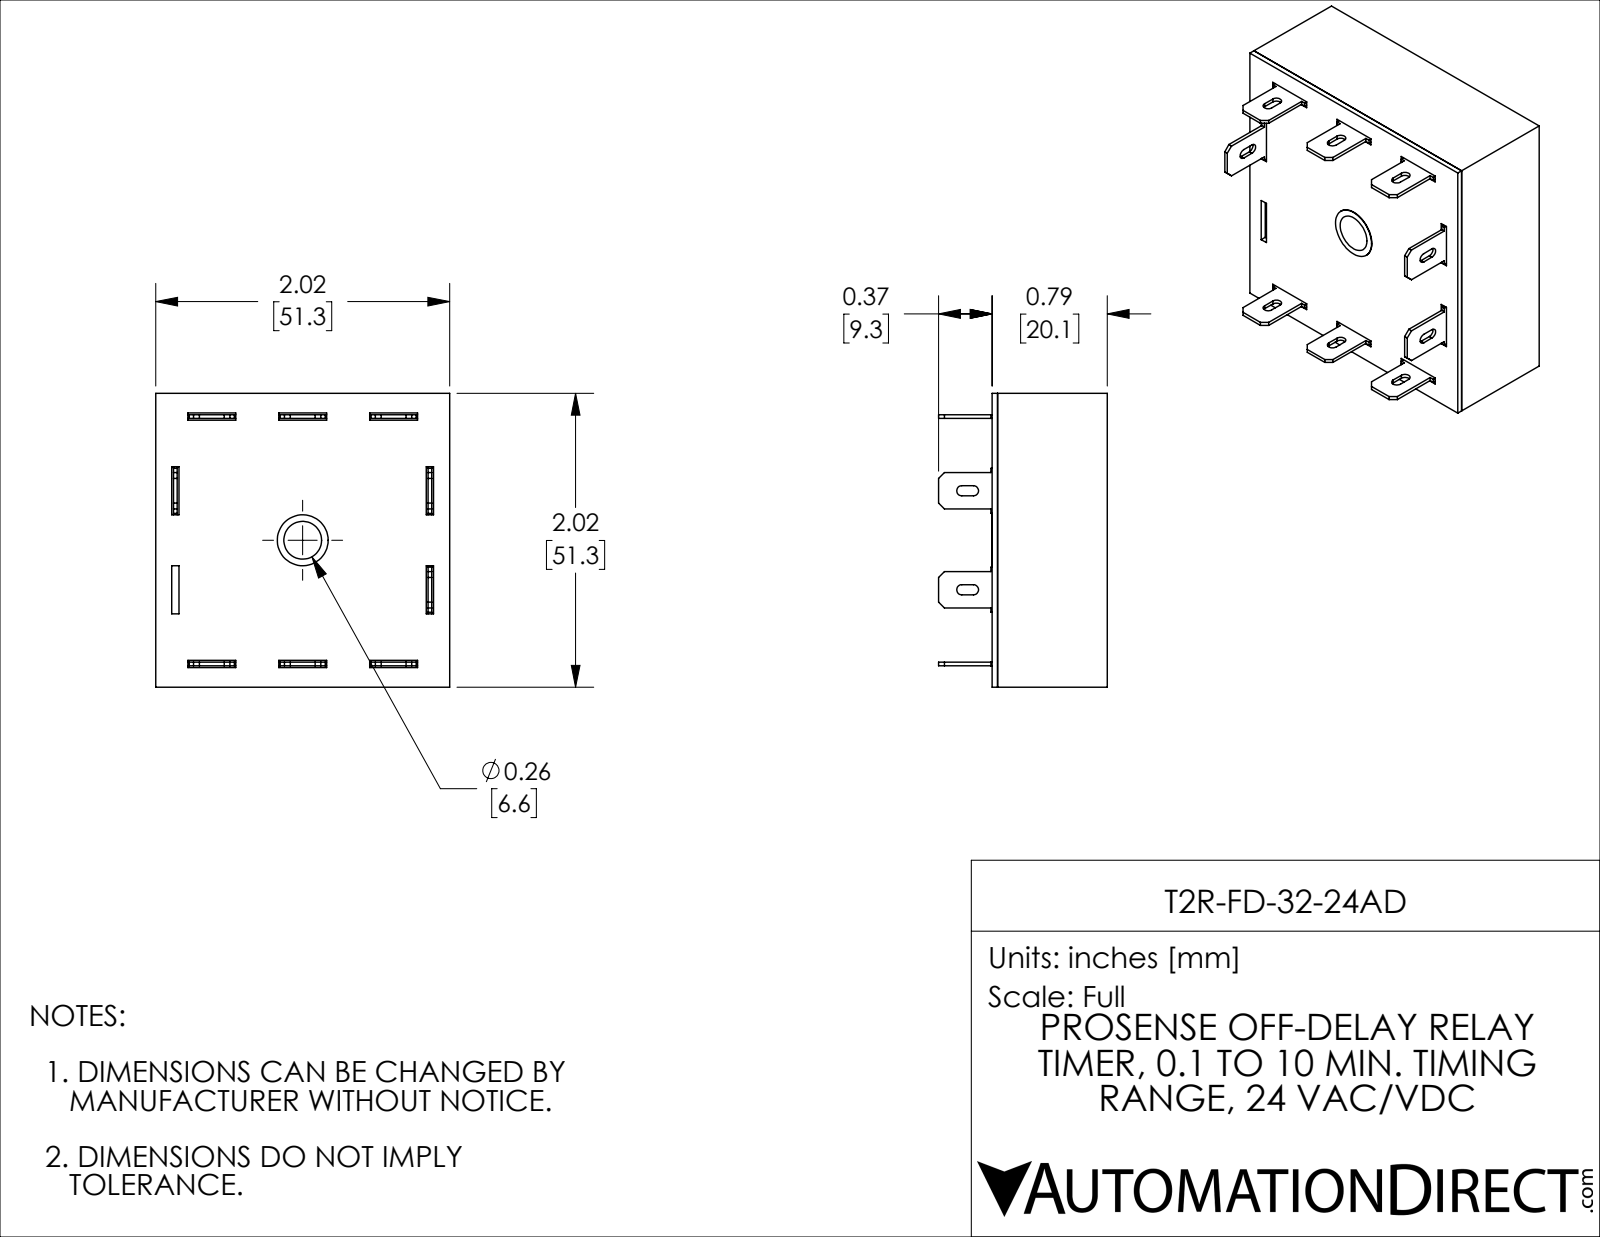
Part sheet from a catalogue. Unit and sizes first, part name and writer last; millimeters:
Units: millimetres
Overall size (bounding box): 51.31 × 51.31 × 29.46
Round holes (diameter × count): ⌀8.89 ×1
Partial cylindrical surfaces — rounded edges, fillets, slot ends (radius × count): R0.89 ×10
Main face-to-face distances: 1.14, 50.16, 19.15, 20.12, 0.97, 18.01, 18.98, 51.3, 3.74, 47.56
Volume: 11 178 mm³ · Surface area: 23 301 mm²
Bodies: 11 solids, 280 faces (256 planar, 22 cylindrical, 2 other)
Part name (STEP PRODUCT): T2R-FD-32-24AD
STEP written by: SolidWorks 2021 (CONFIG_CONTROL_DESIGN)
